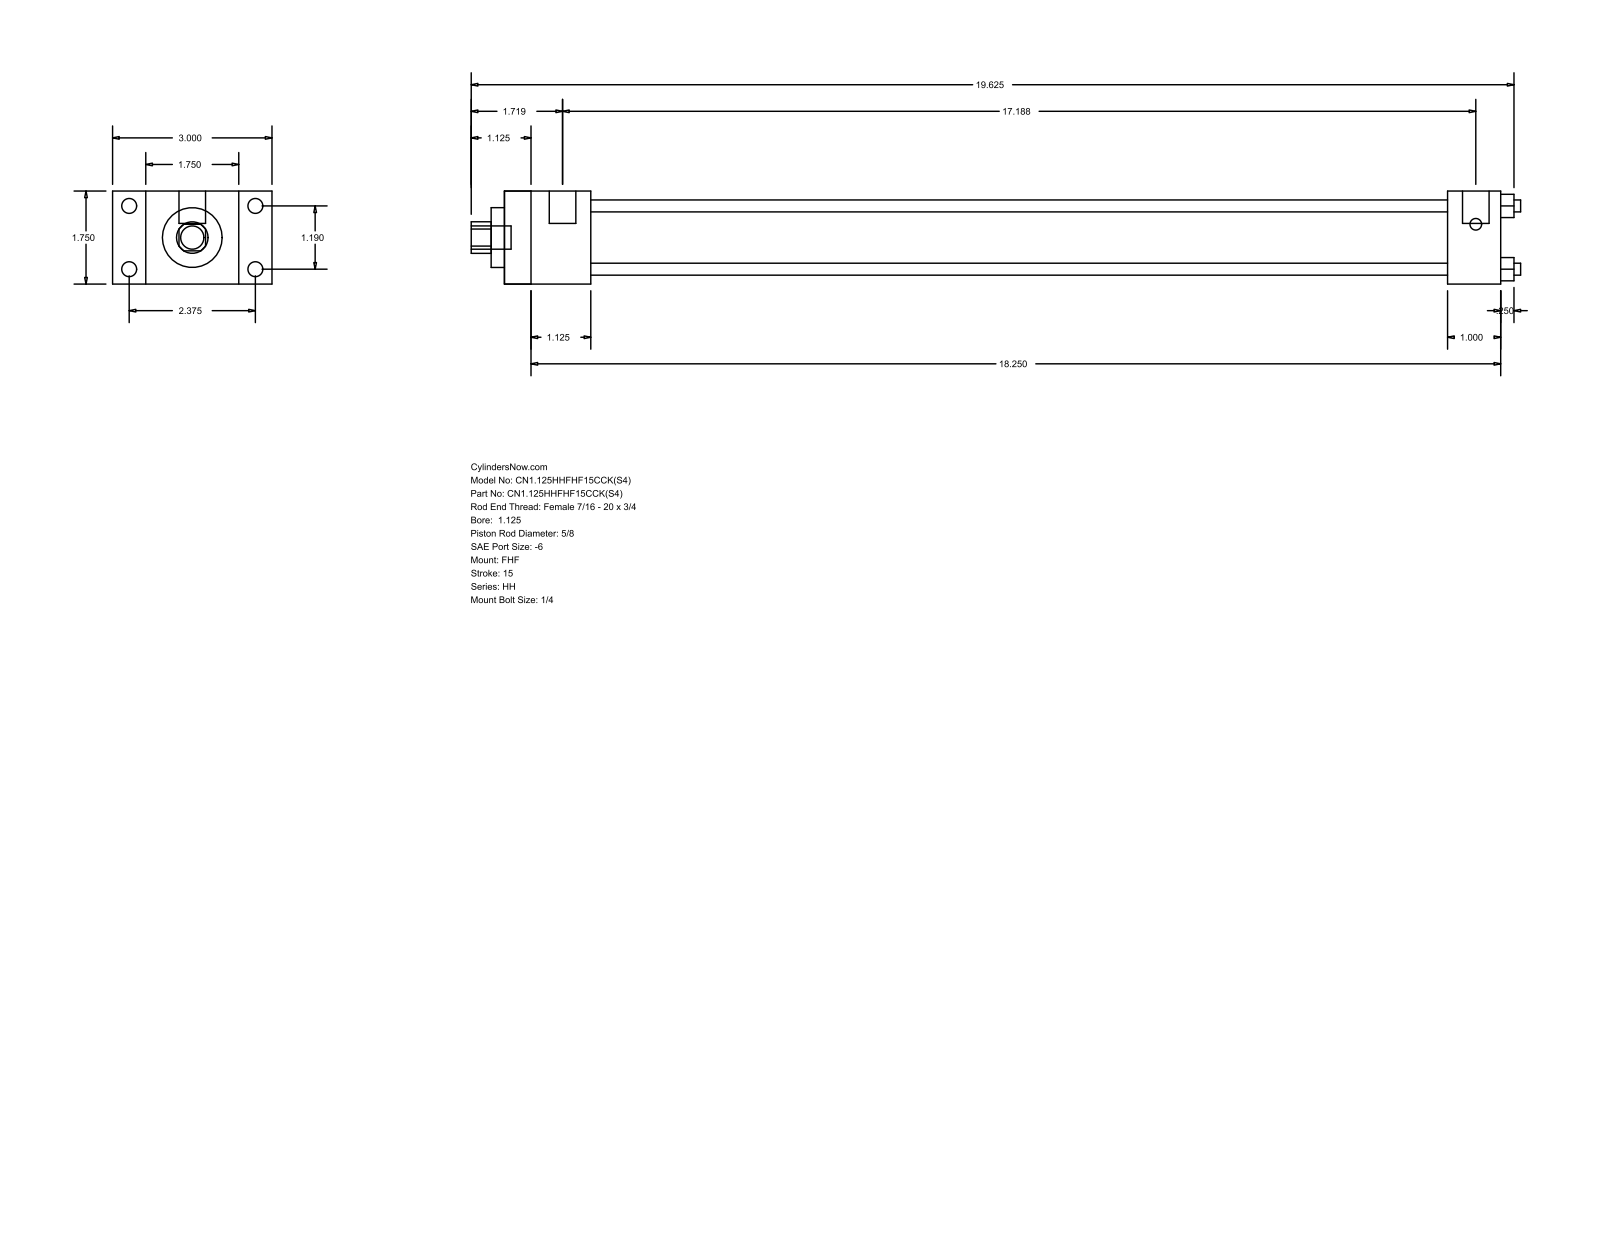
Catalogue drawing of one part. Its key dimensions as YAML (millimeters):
part_name: "HH_FHF__0112_0.625"
step_written_by: "GSSL Pune (CONFIG_CONTROL_DESIGN)"
units: millimeters
bodies: {solids: 0, faces: 88, planar: 60, cylindrical: 28, other: 0}
overall_size: [501.65, 76.2, 44.45]
round_holes:
  - {diameter: 5.71, count: 4}
  - {diameter: 15.88, count: 1}
  - {diameter: 28.57, count: 1}
  - {diameter: 34.92, count: 1}
round_bosses_or_shafts:
  - {diameter: 7.14, count: 4}
  - {diameter: 5.56, count: 4}
  - {diameter: 12.7, count: 2}
  - {diameter: 11.11, count: 1}
partial_cylinders:
  - {radius: 7.54, count: 1}
face_to_face_distances: [44.46, 15.87, 60.33, 41.27, 76.2, 476.24, 434.97, 450.85, 409.58, 25.39]
hole_center_spacings: [21.37, 30.22, 42.74]
